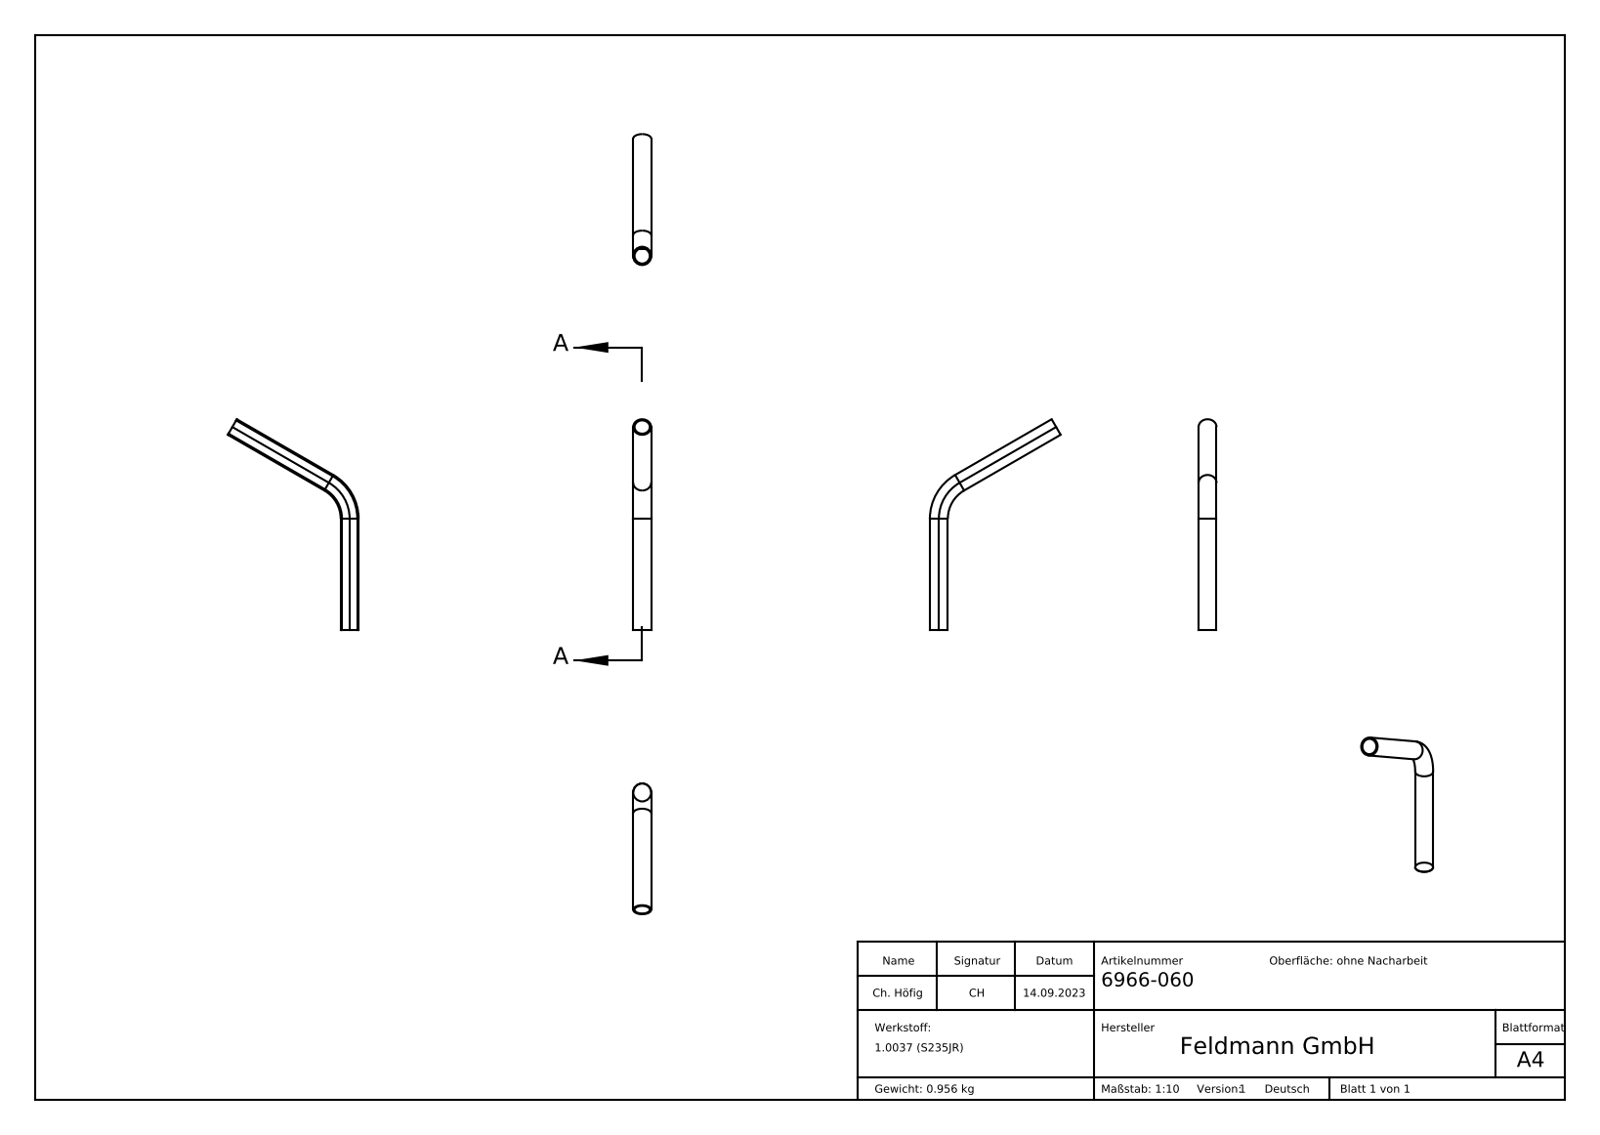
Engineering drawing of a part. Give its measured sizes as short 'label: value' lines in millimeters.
name: 6966-060
written by: SolidWorks 2018 (CONFIG_CONTROL_DESIGN)
unit: mm
bodies: 1 solid, 218 faces (101 planar, 4 cylindrical, 113 other)
size: 395.88 × 245.41 × 33.7
volume: 122 522 mm³; area: 98 511 mm²
holes: 2× ⌀28.7
bosses: 2× ⌀33.7
face distances: 0.34, 0.53, 0.58, 0.31, 0.39, 0.32, 0.48, 0.54, 0.52, 0.47
